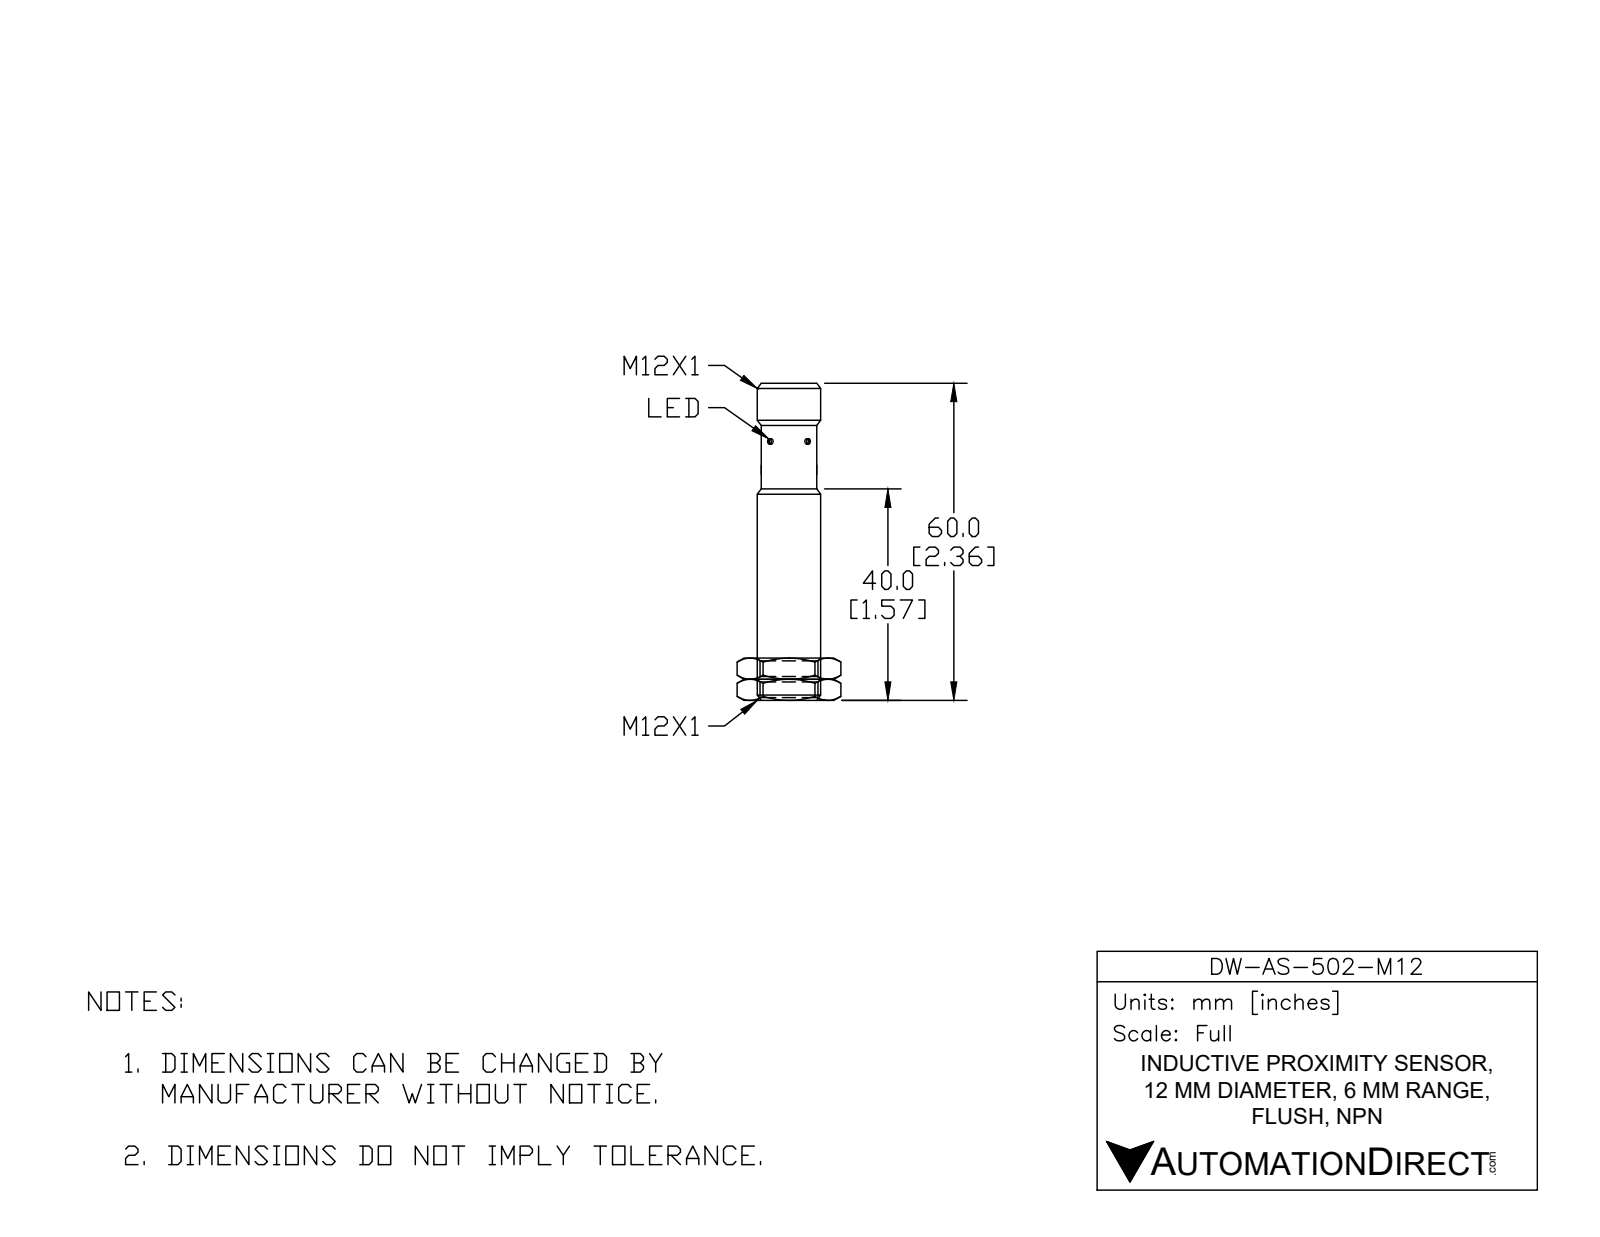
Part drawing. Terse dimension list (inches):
name: DW-AS-502-M12
written by: SolidWorks 2017 (AUTOMOTIVE_DESIGN)
unit: in
bodies: 1 solid, 35 faces (7 planar, 19 cylindrical, 9 other)
size: 2.362 × 0.472 × 0.472
volume: 0.367 in³; area: 4.348 in²
holes: 2× ⌀0.118, 1× ⌀0.335
bosses: 4× ⌀0.039, 1× ⌀0.472, 1× ⌀0.415
rounds: 2× R0.022, 1× R0.193
face distances: 2.02, 2.362, 0.343, 0.043, 1.614, 0.406, 0.748, 2.047, 0.433, 0.028
